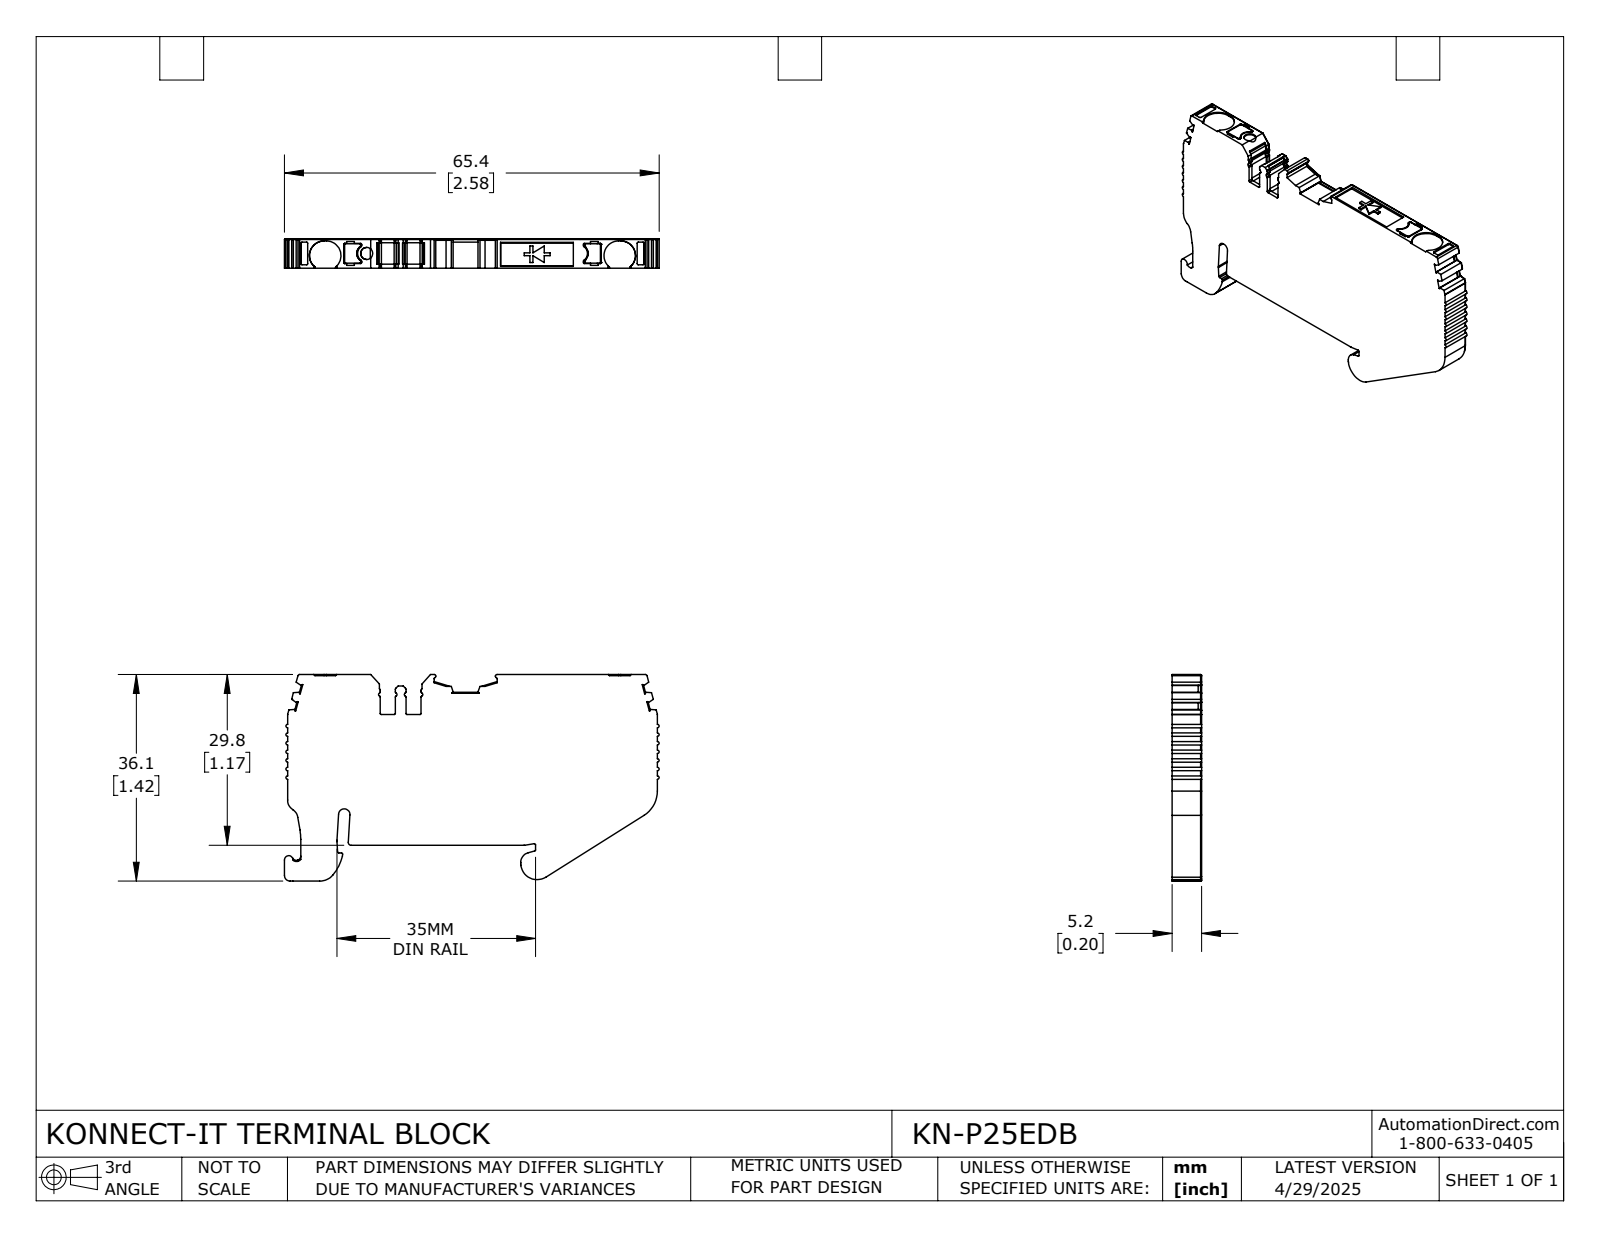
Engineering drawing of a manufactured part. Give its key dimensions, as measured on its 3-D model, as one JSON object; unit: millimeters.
{"part_name": "KN-P25EDB", "step_written_by": "SolidWorks 2024 (CONFIG_CONTROL_DESIGN)", "units": "millimeters", "bodies": {"solids": 1, "faces": 549, "planar": 326, "cylindrical": 220, "other": 3}, "overall_size": [65.42, 36.07, 5.15], "volume_mm3": 9576, "surface_area_mm2": 5137, "round_holes": [[2.1, 1]], "partial_cylinders_radius": [[0.2, 54], [0.3, 39], [0.5, 16], [0.1, 13], [0.4, 9], [0.15, 8], [2.55, 4], [1, 3]], "face_to_face_distances": [5.15, 29.61, 29.81, 64.58, 4.5, 5, 6.26, 35.87, 2, 36.07]}
